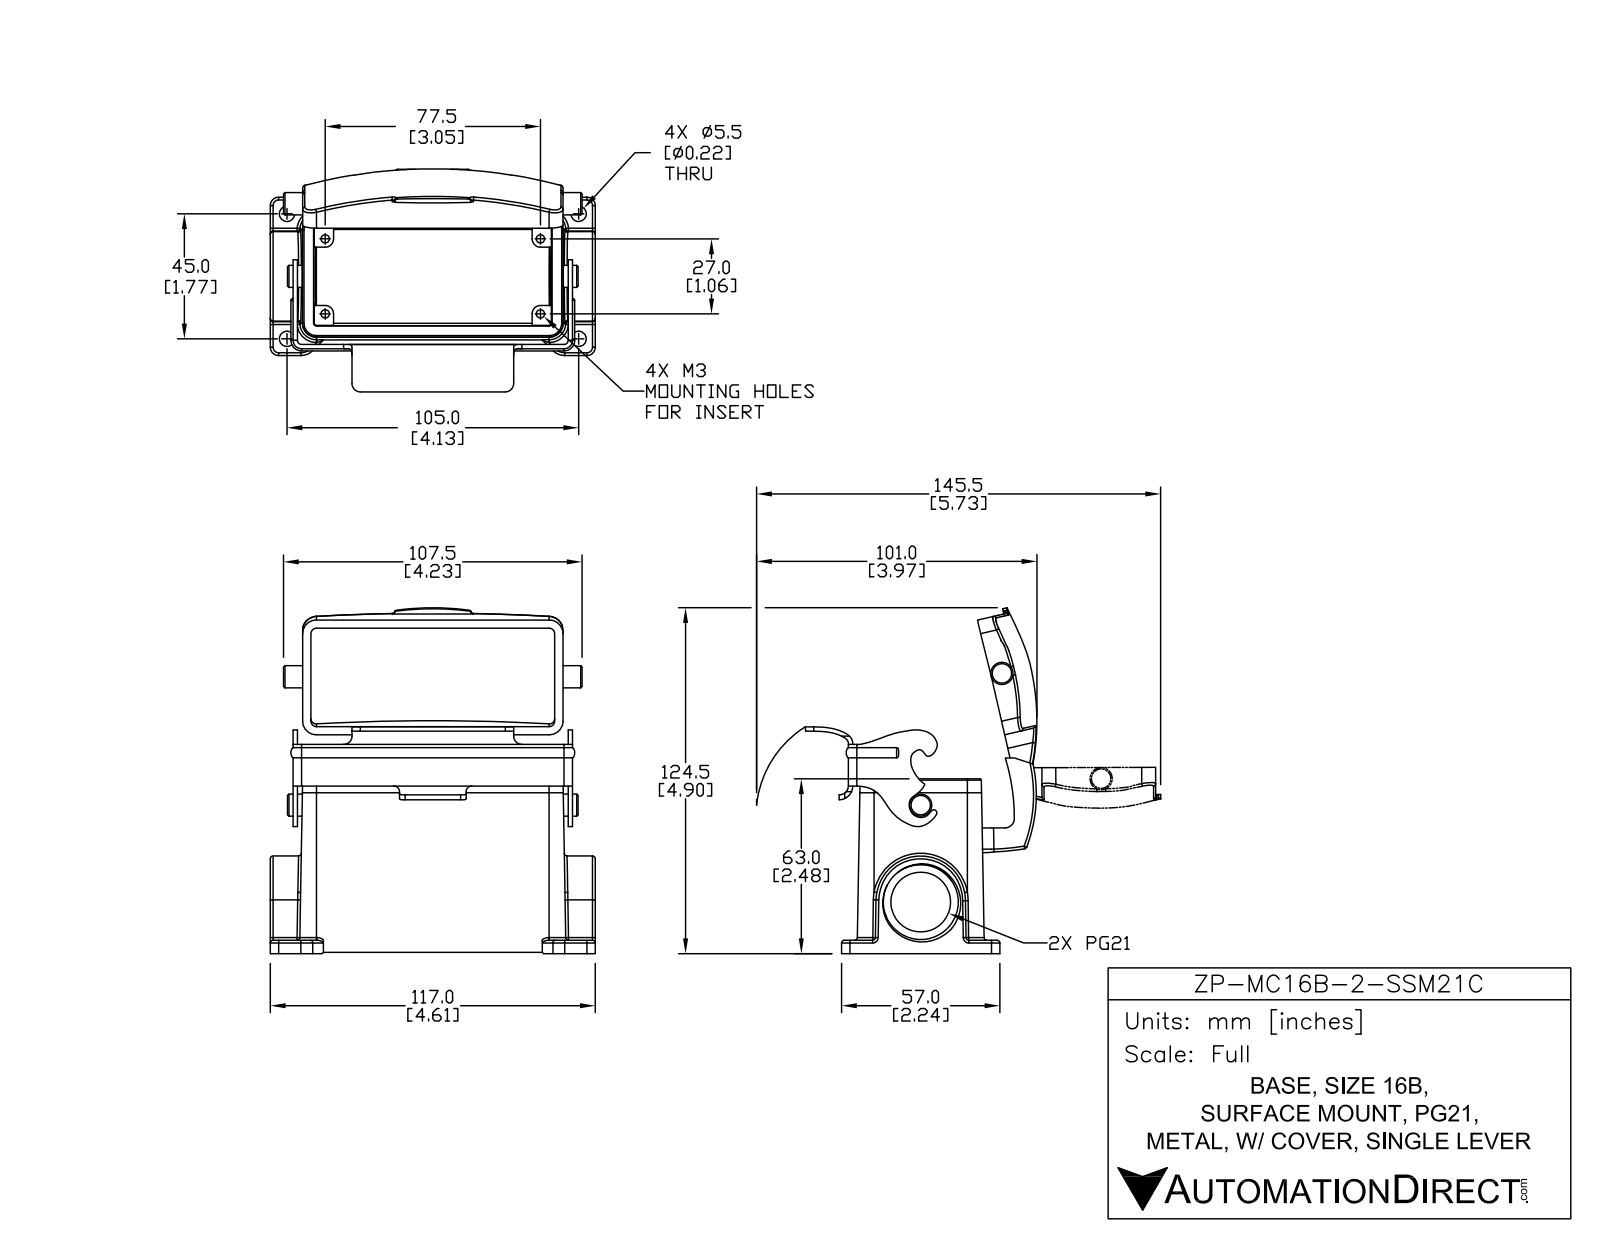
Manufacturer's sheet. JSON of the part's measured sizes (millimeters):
{"part_name": "ZP-MC16B-2-SSM21C", "step_written_by": "SolidWorks 2014 (AUTOMOTIVE_DESIGN)", "units": "millimeters", "bodies": {"solids": 3, "faces": 432, "planar": 146, "cylindrical": 163, "other": 123}, "overall_size": [125.02, 117, 80.31], "volume_mm3": 142789, "surface_area_mm2": 72133, "round_holes": [[3, 4], [5.5, 4], [2, 1], [21.5, 1], [27, 1]], "round_bosses_or_shafts": [[8, 1], [7.95, 1]], "partial_cylinders_radius": [[1, 24], [3, 12], [2, 8], [5, 6], [0.5, 4], [6, 4], [1.5, 2], [3.06, 2]], "face_to_face_distances": [39.67, 5.85, 1.56, 0.5, 6.35, 3, 40.48, 99.06, 89.8, 89.81], "hole_center_spacings": [16.43, 38.54, 91.69, 98.09, 27, 45, 77.5, 82.07]}
